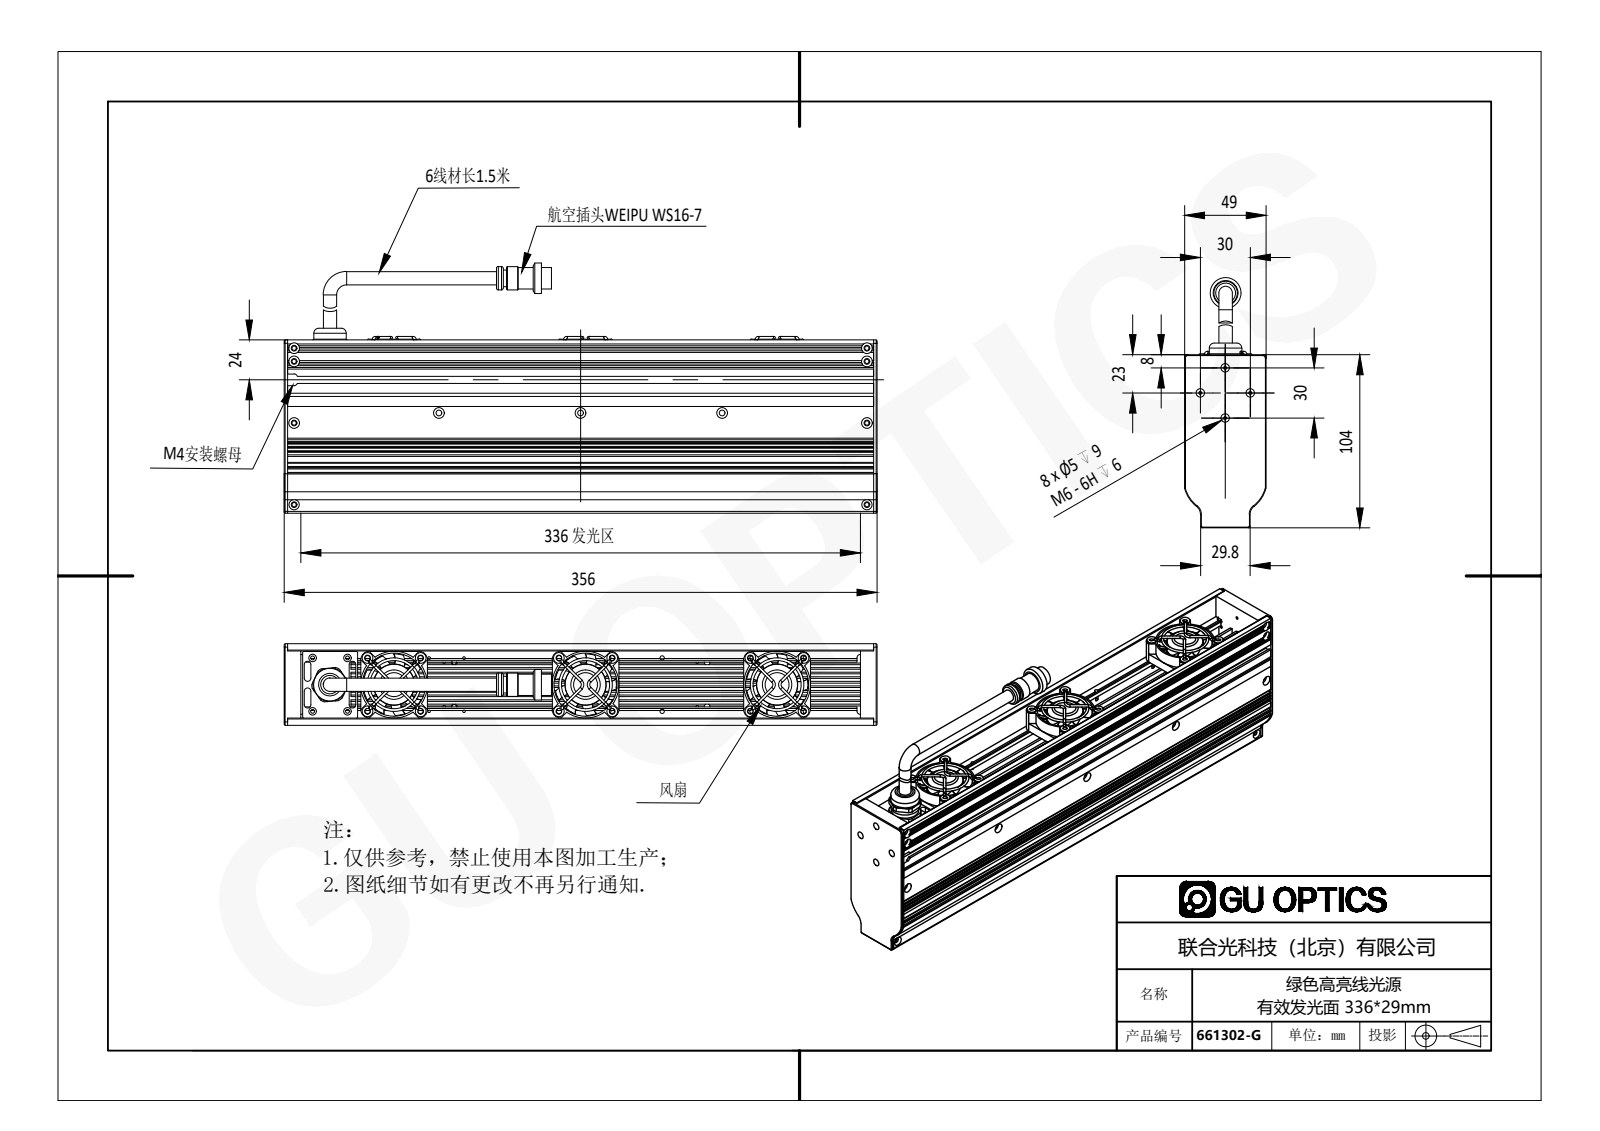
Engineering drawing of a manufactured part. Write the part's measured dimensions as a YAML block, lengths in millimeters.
part_name: "661302-G"
step_written_by: "SolidWorks 2016 (AUTOMOTIVE_DESIGN)"
units: millimeters
bodies: {solids: 26, faces: 2231, planar: 924, cylindrical: 693, other: 614}
overall_size: [356, 150.2, 49]
volume: 895739
surface_area: 432227
round_holes:
  - {diameter: 2.5, count: 25}
  - {diameter: 3.2, count: 12}
  - {diameter: 6.2, count: 12}
  - {diameter: 3.4, count: 11}
  - {diameter: 1.6, count: 10}
  - {diameter: 3.5, count: 10}
  - {diameter: 6.5, count: 9}
  - {diameter: 1, count: 6}
  - {diameter: 2.4, count: 4}
  - {diameter: 5, count: 4}
  - {diameter: 38, count: 3}
  - {diameter: 11, count: 1}
round_bosses_or_shafts:
  - {diameter: 1.6, count: 12}
  - {diameter: 24.8, count: 3}
  - {diameter: 24, count: 3}
  - {diameter: 2, count: 3}
  - {diameter: 8, count: 2}
  - {diameter: 35, count: 1}
  - {diameter: 19.5, count: 1}
  - {diameter: 19, count: 1}
partial_cylinders:
  - {radius: 1, count: 58}
  - {radius: 0.2, count: 28}
  - {radius: 2, count: 20}
  - {radius: 5.1, count: 13}
  - {radius: 0.4, count: 12}
  - {radius: 0.5, count: 10}
  - {radius: 3, count: 7}
  - {radius: 1.11, count: 6}
face_to_face_distances: [5.5, 2, 5, 1.7, 11, 5.1, 43.9, 7.2, 48.9, 43.8]
hole_center_spacings: [32, 3.5, 31.82, 45, 86, 26.8, 70, 3.51]
